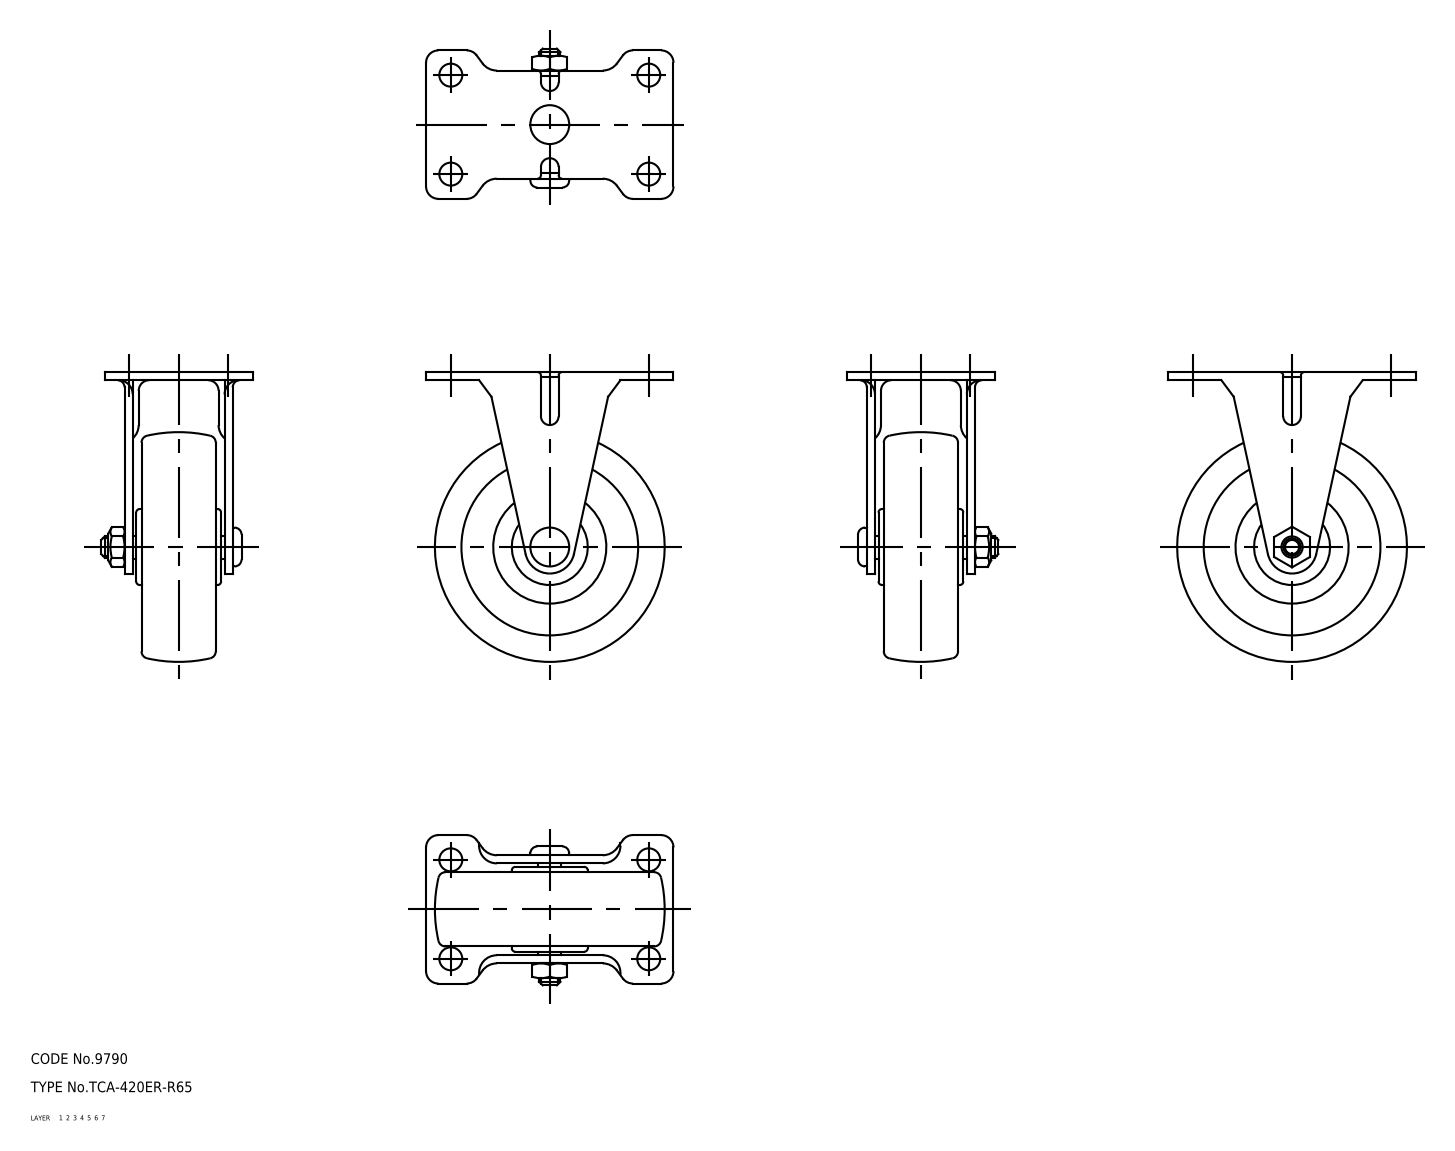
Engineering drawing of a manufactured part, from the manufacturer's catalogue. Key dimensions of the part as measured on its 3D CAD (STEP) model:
Part name (STEP PRODUCT): wheel; axle; No_420_ER_R65_2_30758_36
STEP written by: CADfix (AUTOMOTIVE_DESIGN)
Units: millimetres
Bodies: 3 solids, 176 faces (0 planar, 0 cylindrical, 176 other)
Overall size (bounding box): 82 × 70 × 42.9
Volume: 75 809 mm³ · Surface area: 23 148 mm²
